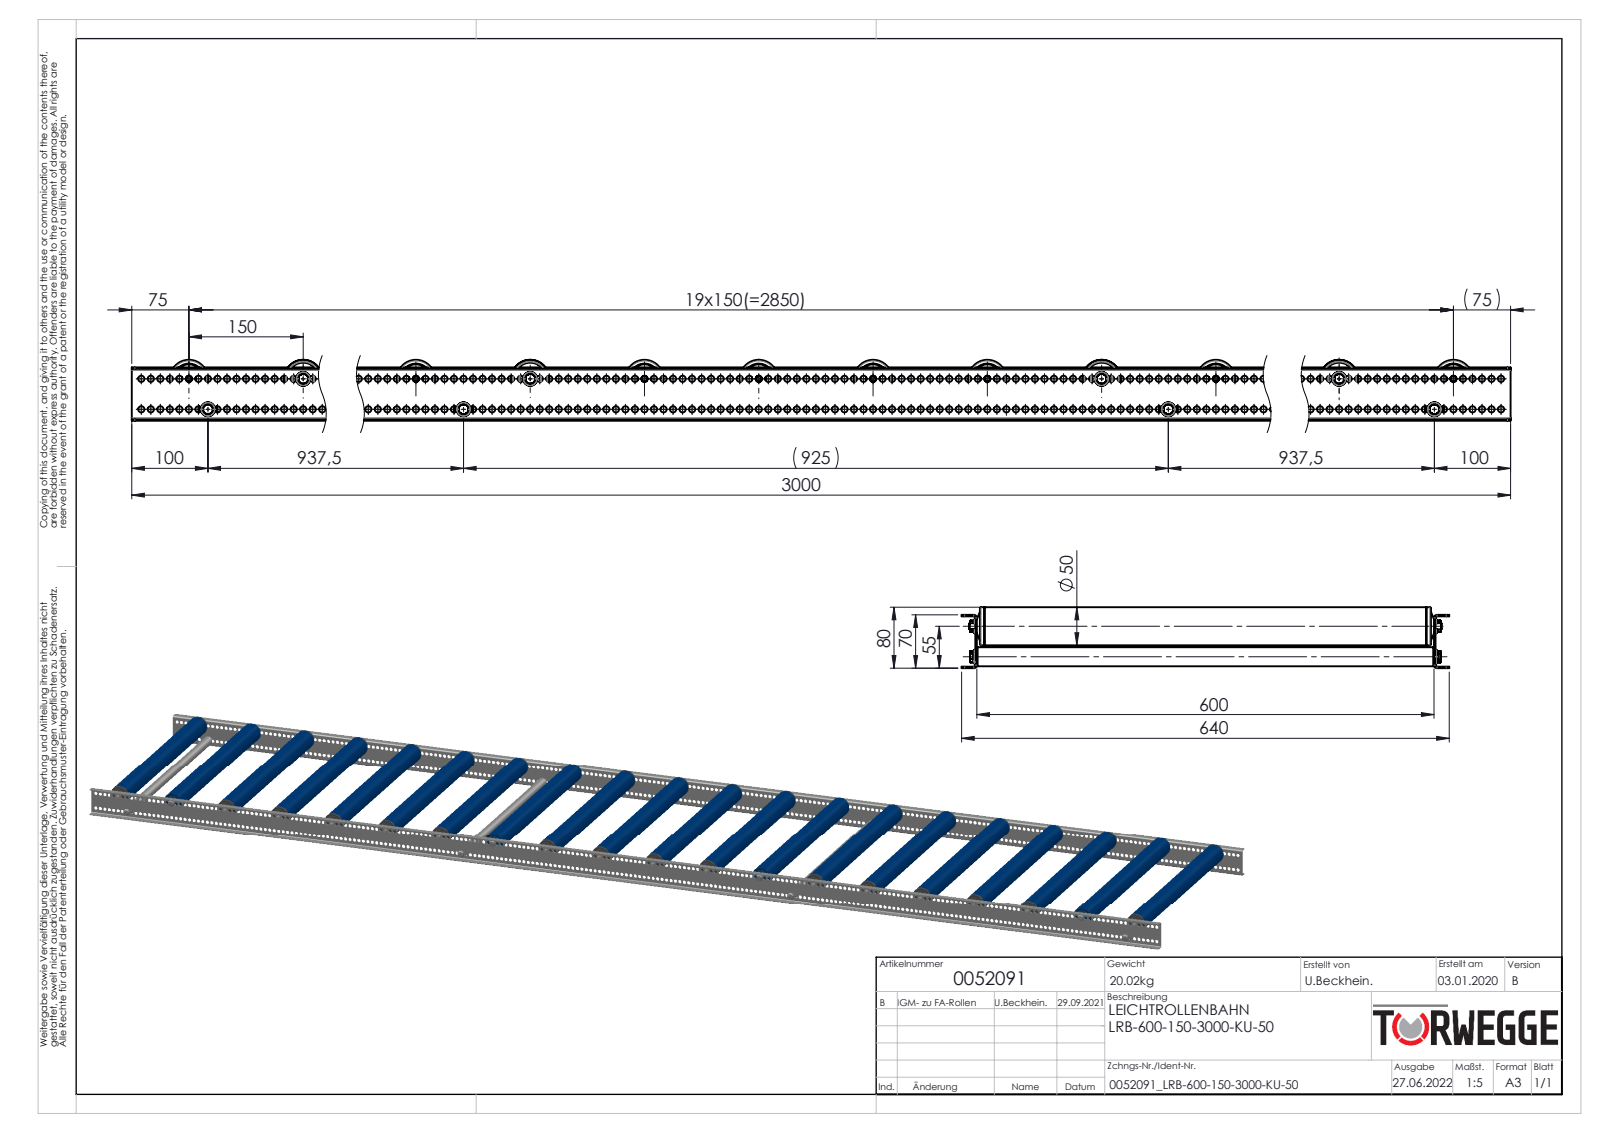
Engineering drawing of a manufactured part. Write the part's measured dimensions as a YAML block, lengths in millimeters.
part_name: "Traversen_KFG_L600; 0017015_Tragrollenrohr-Ø50x2,8KU_KFG_0017015_L=585; Druckfeder_1,2x10x30; KUT100-50x2,8-KB-A8-FA_KFG_0034516_KUT100-50x2,8-KB-A8-FA-EL=600 (+8 more)"
step_written_by: "SolidWorks 2020 (AUTOMOTIVE_DESIGN)"
units: millimeters
bodies: {solids: 414, faces: 8500, planar: 2012, cylindrical: 3960, other: 2528}
overall_size: [3000, 640, 80]
volume: 8187000
surface_area: 6215000
round_holes:
  - {diameter: 8.2, count: 478}
  - {diameter: 7.6, count: 16}
  - {diameter: 8, count: 16}
  - {diameter: 25, count: 16}
  - {diameter: 30, count: 16}
  - {diameter: 35, count: 16}
  - {diameter: 39.4, count: 16}
  - {diameter: 40, count: 16}
  - {diameter: 6.8, count: 8}
  - {diameter: 12, count: 4}
  - {diameter: 12.1, count: 4}
  - {diameter: 16, count: 4}
round_bosses_or_shafts:
  - {diameter: 50, count: 20}
  - {diameter: 44.4, count: 16}
  - {diameter: 38, count: 16}
  - {diameter: 36, count: 16}
  - {diameter: 33, count: 16}
  - {diameter: 22, count: 16}
  - {diameter: 21, count: 16}
  - {diameter: 25, count: 8}
partial_cylinders:
  - {radius: 0.6, count: 32}
  - {radius: 0.75, count: 32}
  - {radius: 2.45, count: 32}
  - {radius: 2.5, count: 16}
  - {radius: 4.87, count: 16}
  - {radius: 7, count: 16}
  - {radius: 4, count: 8}
  - {radius: 2, count: 4}
face_to_face_distances: [2, 602, 68, 600, 604, 70, 66, 6, 592, 12]
hole_center_spacings: [12.5, 25, 37.5, 50, 62.5, 75, 87.5, 100]
